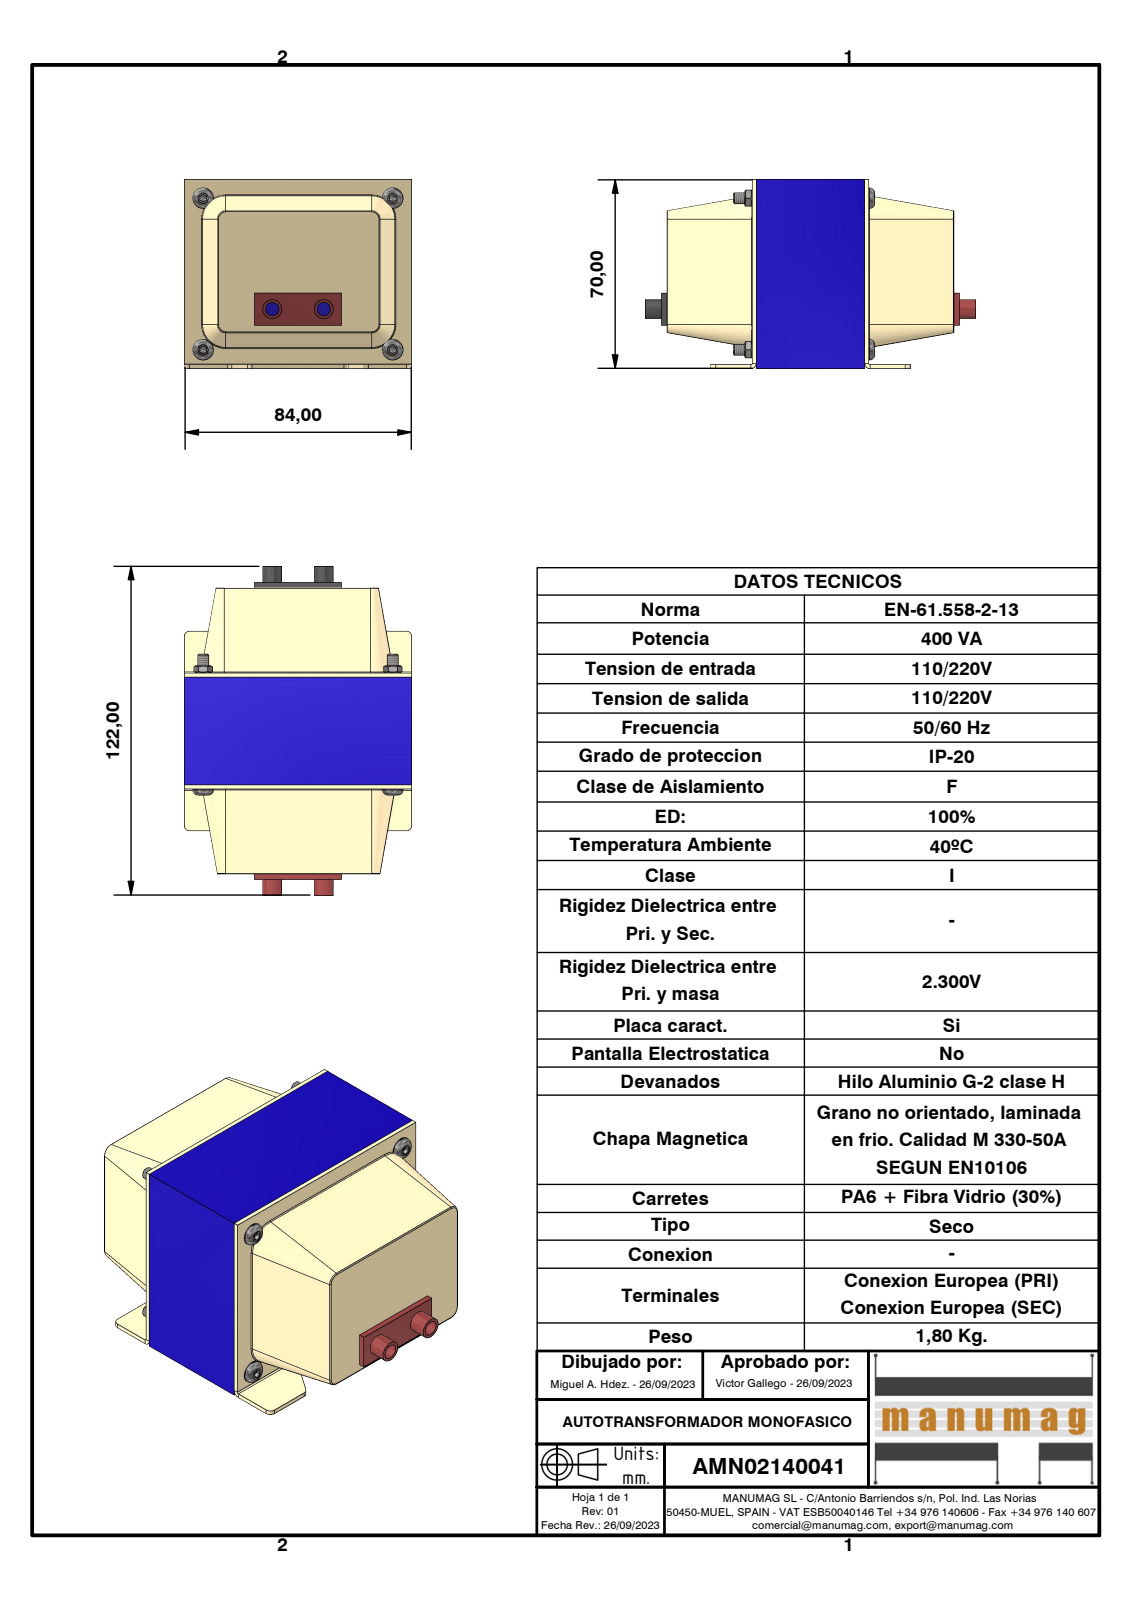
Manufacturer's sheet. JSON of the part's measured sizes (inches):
{"part_name": "AMN02140041; EI84 x 70 - 40 (RC28) Azul; TAPA RC28 RECEPTACULO; Receptaculo negro (+3 more)", "step_written_by": "Autodesk Inventor 2023 (AUTOMOTIVE_DESIGN)", "units": "inches", "bodies": {"solids": 13, "faces": 286, "planar": 158, "cylindrical": 64, "other": 64}, "overall_size": [4.803, 3.307, 2.756], "volume_in3": 12.77, "surface_area_in2": 138, "round_holes": [[0.157, 8], [0.112, 4], [0.177, 4], [0.197, 2]], "round_bosses_or_shafts": [[0.299, 4], [0.276, 2]], "partial_cylinders_radius": [[0.015, 16], [0.079, 14], [0.02, 2]], "face_to_face_distances": [0.059, 0.551, 2.874, 1.24, 2.205, 2.756, 2.461, 1.575, 1.102, 1.299], "hole_center_spacings": [2.756, 3.529, 1.849, 2.205, 1.165, 1.165, 1.9, 1.901]}
